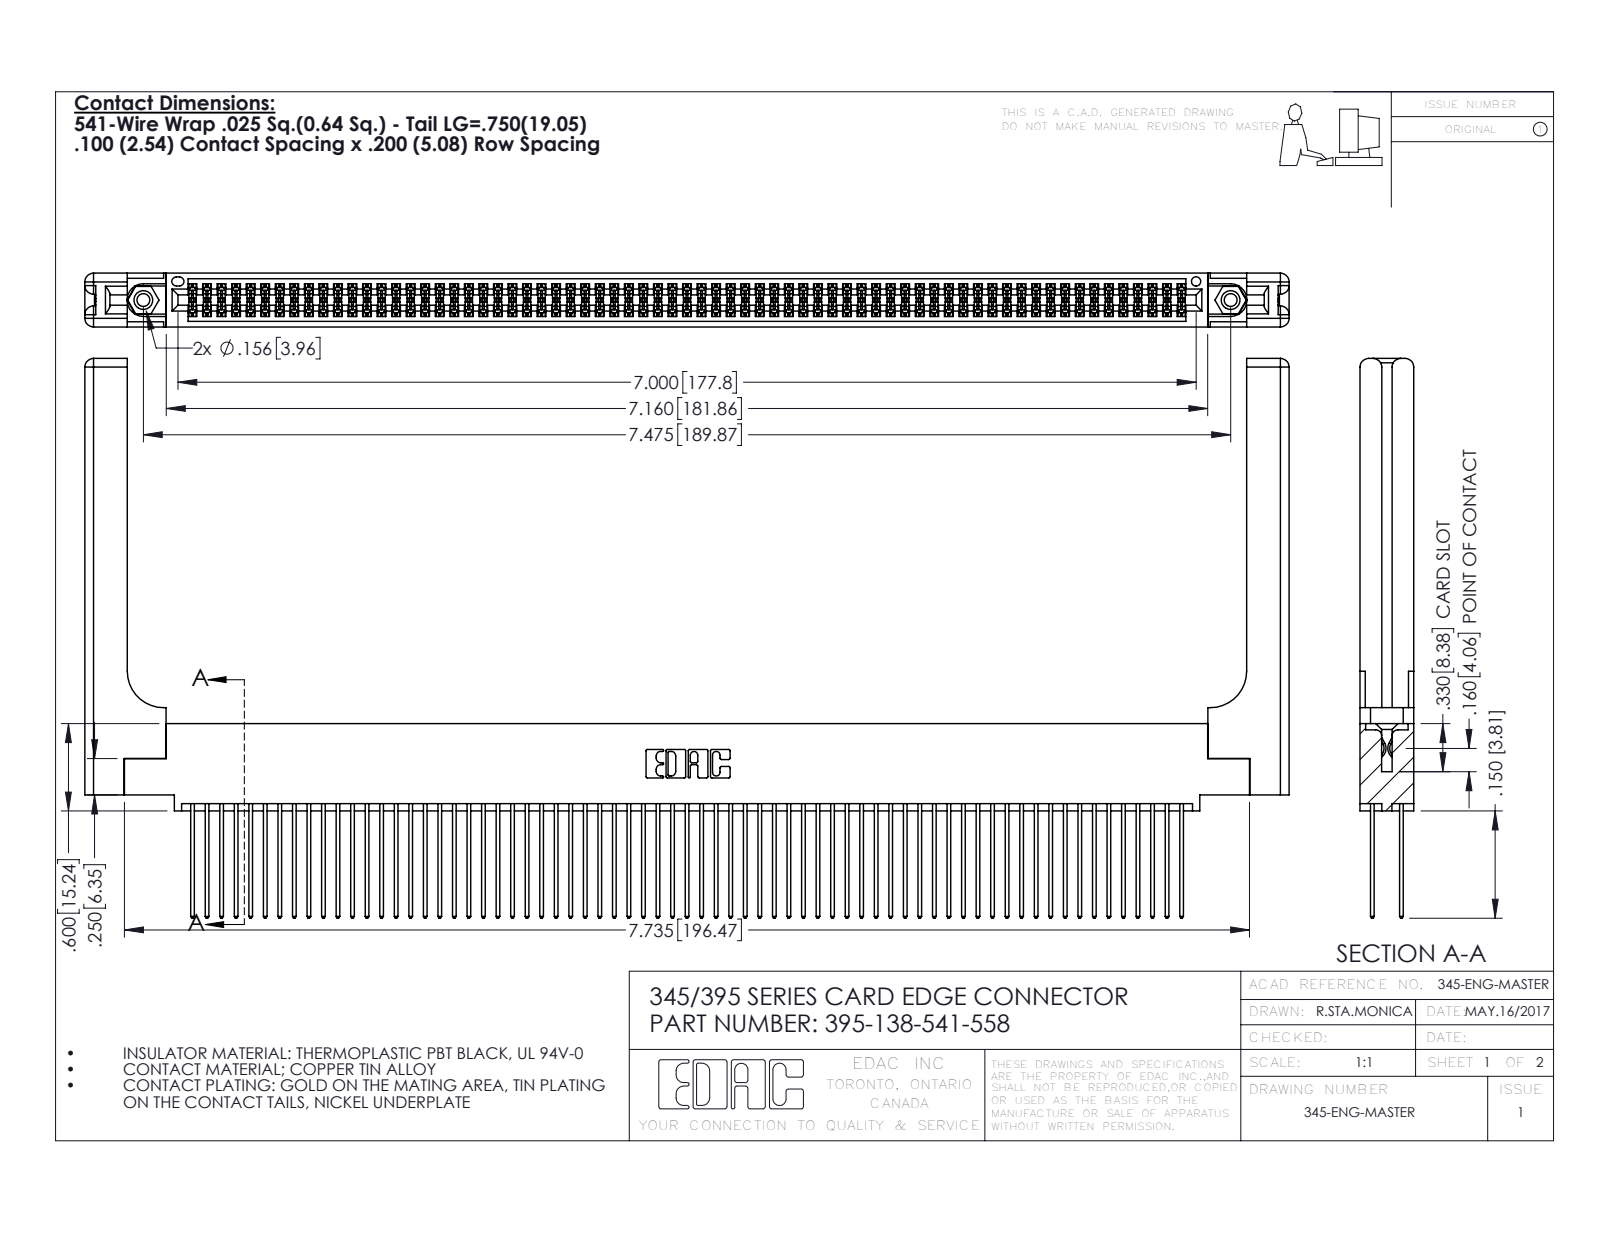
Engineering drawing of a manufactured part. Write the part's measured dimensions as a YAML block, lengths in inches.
part_name: "345 Part_0.110 Offset - 0.156 Dia-TH; 345-250-001_345-250-001-102; 345-292-001_345-293-141; 395-138-541-558 (+1 more)"
step_written_by: "SolidWorks 2016 (CONFIG_CONTROL_DESIGN)"
units: inches
bodies: {solids: 143, faces: 7286, planar: 4786, cylindrical: 2440, other: 60}
overall_size: [8.279, 3.847, 0.37]
volume: 1.823
surface_area: 63.59
round_holes:
  - {diameter: 0.089, count: 2}
  - {diameter: 0.125, count: 2}
  - {diameter: 0.156, count: 2}
  - {diameter: 0.064, count: 1}
round_bosses_or_shafts:
  - {diameter: 0.155, count: 2}
partial_cylinders:
  - {radius: 0.006, count: 207}
  - {radius: 0.01, count: 138}
  - {radius: 0.01, count: 22}
  - {radius: 0.06, count: 16}
  - {radius: 0.007, count: 6}
  - {radius: 0.031, count: 6}
  - {radius: 0.026, count: 3}
  - {radius: 0.014, count: 2}
face_to_face_distances: [0.072, 0.298, 0.098, 0.272, 0.025, 0.2, 0.37, 0.225, 0.175, 0.148]
hole_center_spacings: [0.27, 7.239, 7.475]
